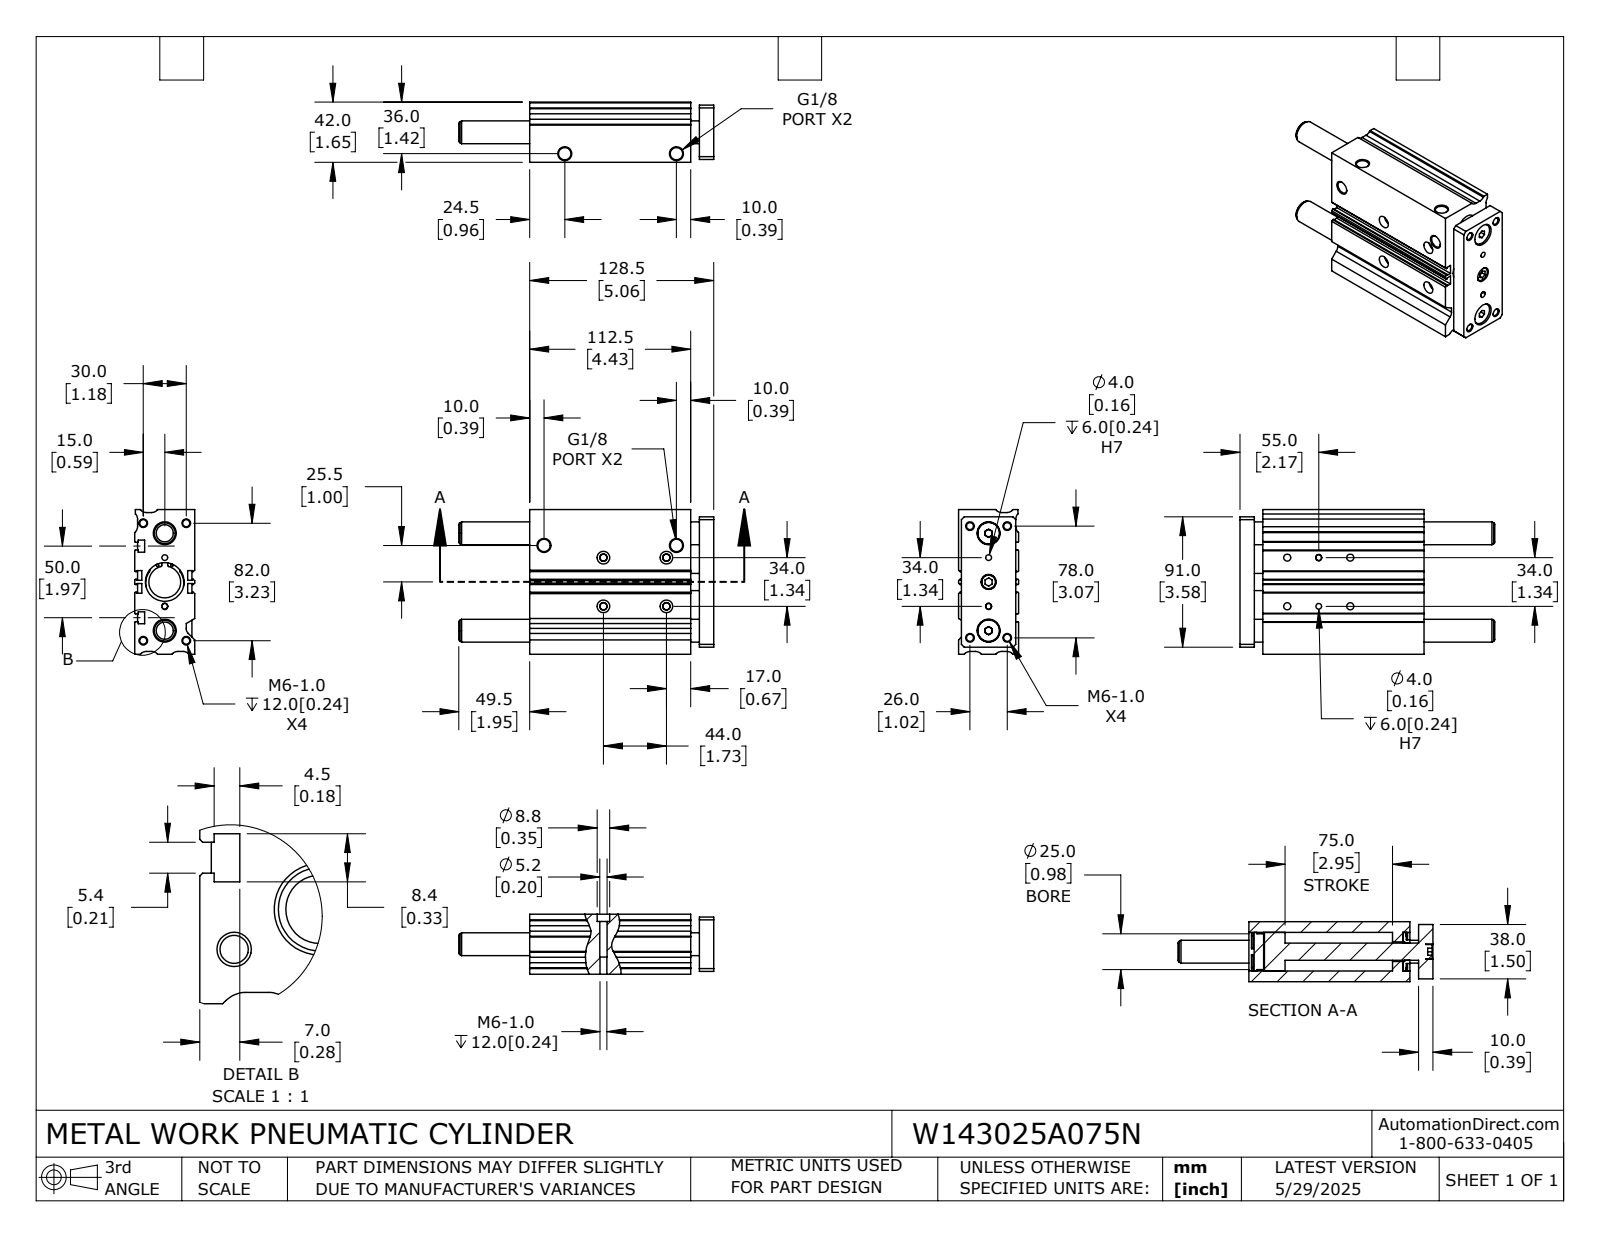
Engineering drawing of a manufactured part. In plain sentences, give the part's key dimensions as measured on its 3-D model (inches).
The part is named "W143025A075N_ROD; W143025A075N; W143025A075N_BODY". Its 3-D file was written by "SolidWorks 2024 (CONFIG_CONTROL_DESIGN)". It is 6 solids with 390 faces: 191 planar, 157 cylindrical and 42 other. Overall it measures 7.008 by 3.976 by 1.654 inches. Its volume is 27.23 cubic inches and its surface area 175.3 square inches. Round holes: 8 of diameter 0.194, 4 of diameter 0.067, 4 of diameter 0.157, 4 of diameter 0.194, 4 of diameter 0.205, 4 of diameter 0.337, 4 of diameter 0.346, 2 of diameter 0.63, 1 of diameter 0.413, 1 of diameter 0.472, 1 of diameter 0.539, 1 of diameter 0.874. Round bosses or shafts: 2 of diameter 0.61, 1 of diameter 1.063, 1 of diameter 0.984, 1 of diameter 0.65, 1 of diameter 0.394. Partial cylindrical surfaces (rounded edges, fillets, slot ends): 12 of radius 0.039, 9 of radius 0.197, 8 of radius 0.079, 2 of radius 0.524, 1 of radius 0.559. The main face-to-face distances are 1.654, 0.197, 0.079, 1.378, 0.118, 0.236, 1.457, 0.63, 0.394, 5.059. The hole center spacings are 1.339, 0.111, 0.29, 0.5, 0.548, 0.652, 0.669, 0.866.
